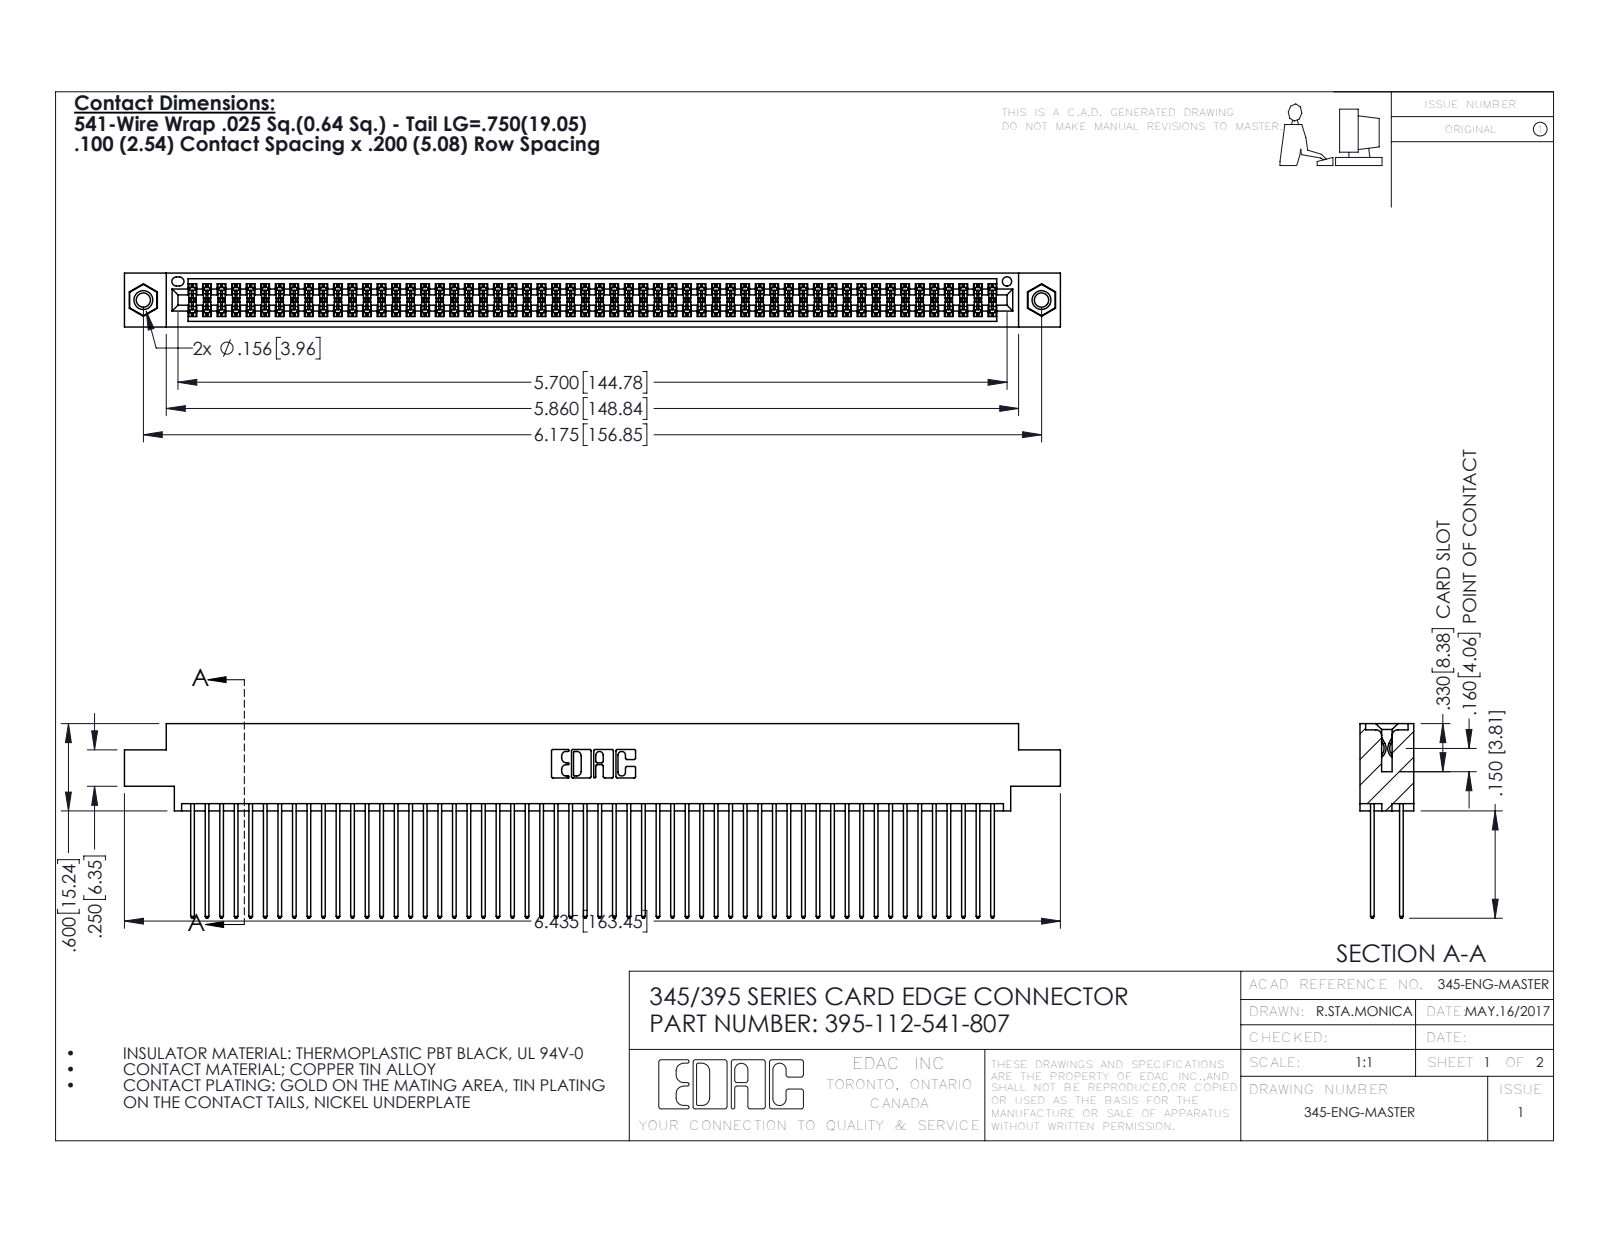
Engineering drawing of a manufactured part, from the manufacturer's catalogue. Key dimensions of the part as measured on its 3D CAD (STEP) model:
Part name (STEP PRODUCT): 345-250-001_345-250-005-103; 345 Part_0.170 Offset - 0.156 Dia-TI; 345-292-001_345-293-141; 395-112-541-807
STEP written by: SolidWorks 2016 (CONFIG_CONTROL_DESIGN)
Units: inches
Bodies: 115 solids, 5790 faces (3812 planar, 1962 cylindrical, 16 other)
Overall size (bounding box): 6.435 × 1.337 × 0.37
Volume: 1.008 in³ · Surface area: 43.23 in²
Round holes (diameter × count): ⌀0.098 ×2, ⌀0.125 ×2, ⌀0.156 ×2, ⌀0.064 ×1
Round bosses / shafts (diameter × count): ⌀0.155 ×2
Partial cylindrical surfaces — rounded edges, fillets, slot ends (radius × count): R0.006 ×168, R0.01 ×112, R0.01 ×22, R0.007 ×6, R0.031 ×6, R0.026 ×3, R0.014 ×2, R0.019 ×2
Main face-to-face distances: 0.072, 0.298, 0.2, 0.098, 0.272, 0.025, 0.225, 0.37, 0.175, 0.149
Hole centre spacings: 0.27, 5.939, 6.175
